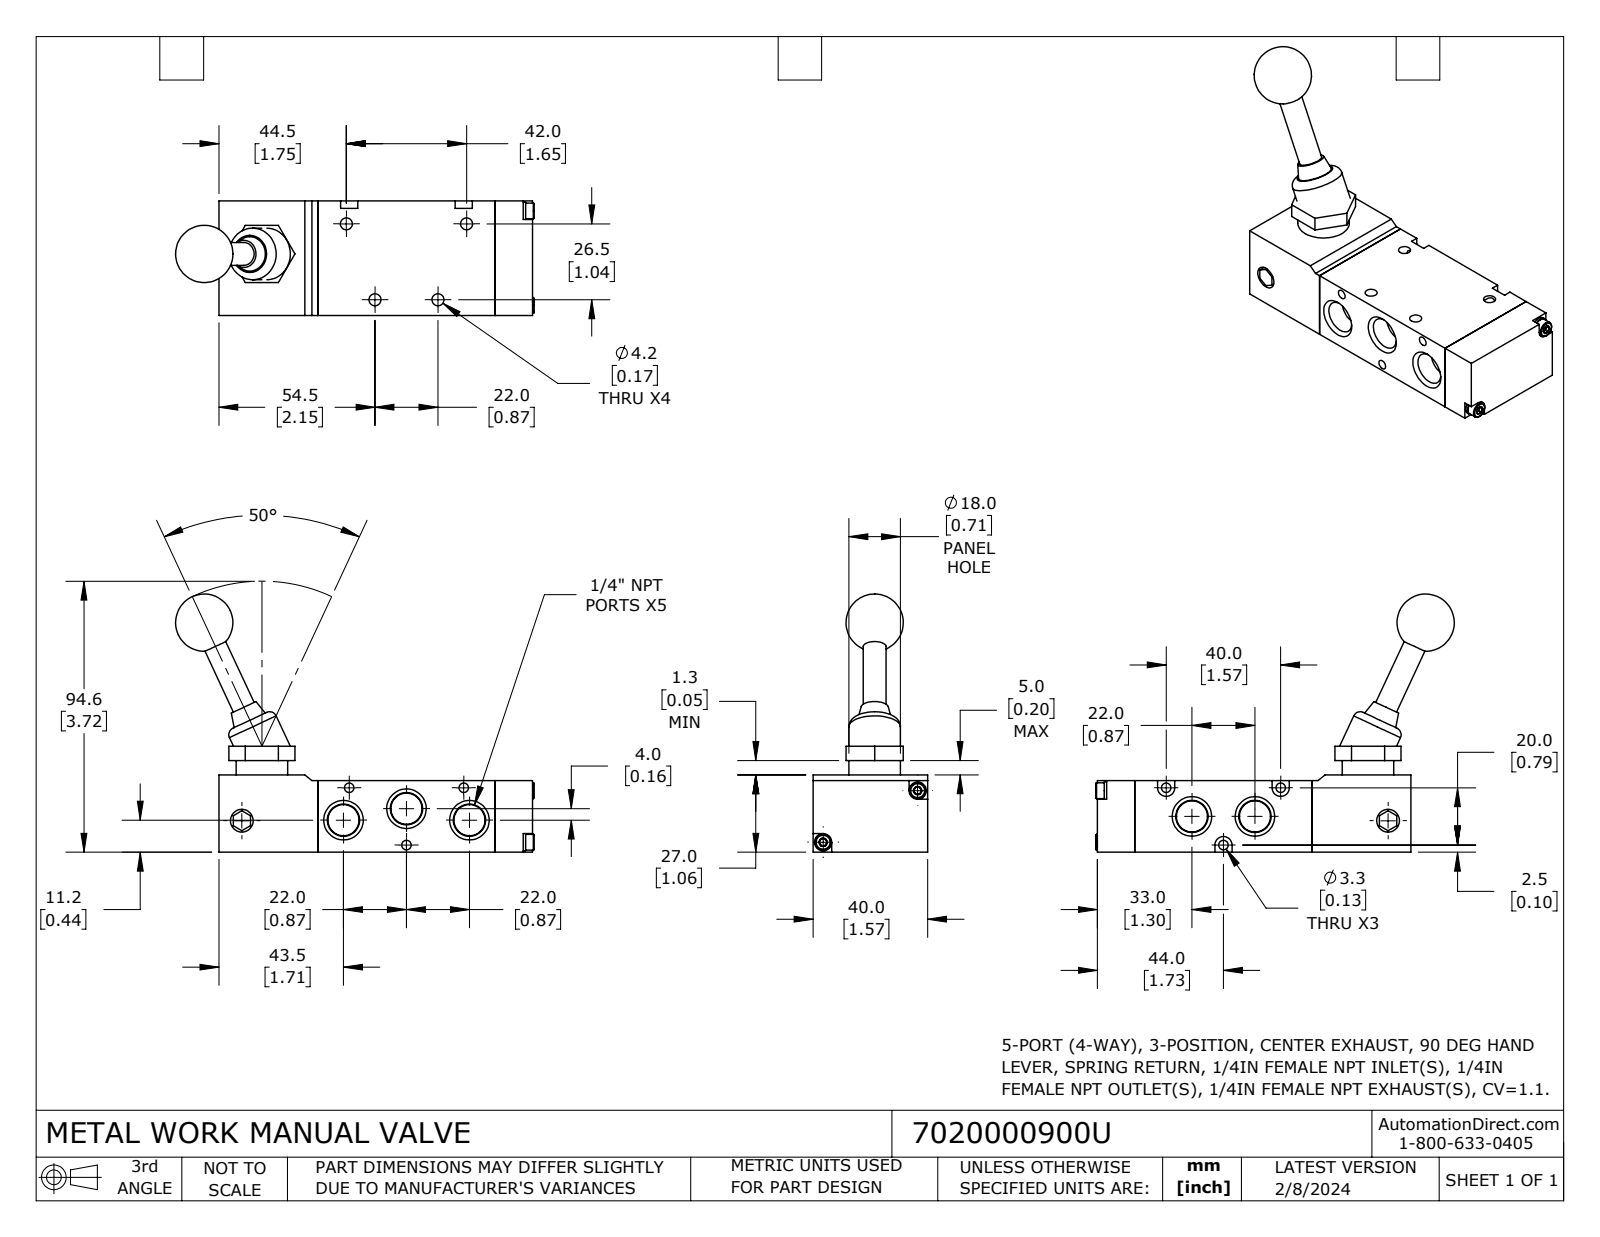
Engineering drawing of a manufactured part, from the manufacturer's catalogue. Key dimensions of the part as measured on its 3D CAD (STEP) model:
Part name (STEP PRODUCT): 7020000900U
STEP written by: SolidWorks 2023 (CONFIG_CONTROL_DESIGN)
Units: inches
Bodies: 8 solids, 206 faces (101 planar, 51 cylindrical, 54 other)
Overall size (bounding box): 4.93 × 3.549 × 1.575
Volume: 7.193 in³ · Surface area: 44.53 in²
Round holes (diameter × count): ⌀0.165 ×4, ⌀0.13 ×3, ⌀0.118 ×2, ⌀0.313 ×1
Round bosses / shafts (diameter × count): ⌀0.709 ×2, ⌀0.236 ×2, ⌀0.217 ×2, ⌀0.315 ×1
Partial cylindrical surfaces — rounded edges, fillets, slot ends (radius × count): R0.118 ×3
Main face-to-face distances: 0.984, 1.575, 2.441, 3.799, 1.358, 1.063, 0.079, 0.512, 2.953, 4.311
Hole centre spacings: 1.113, 1.115, 1.636, 0.866, 1.48, 1.544, 1.575, 1.654
